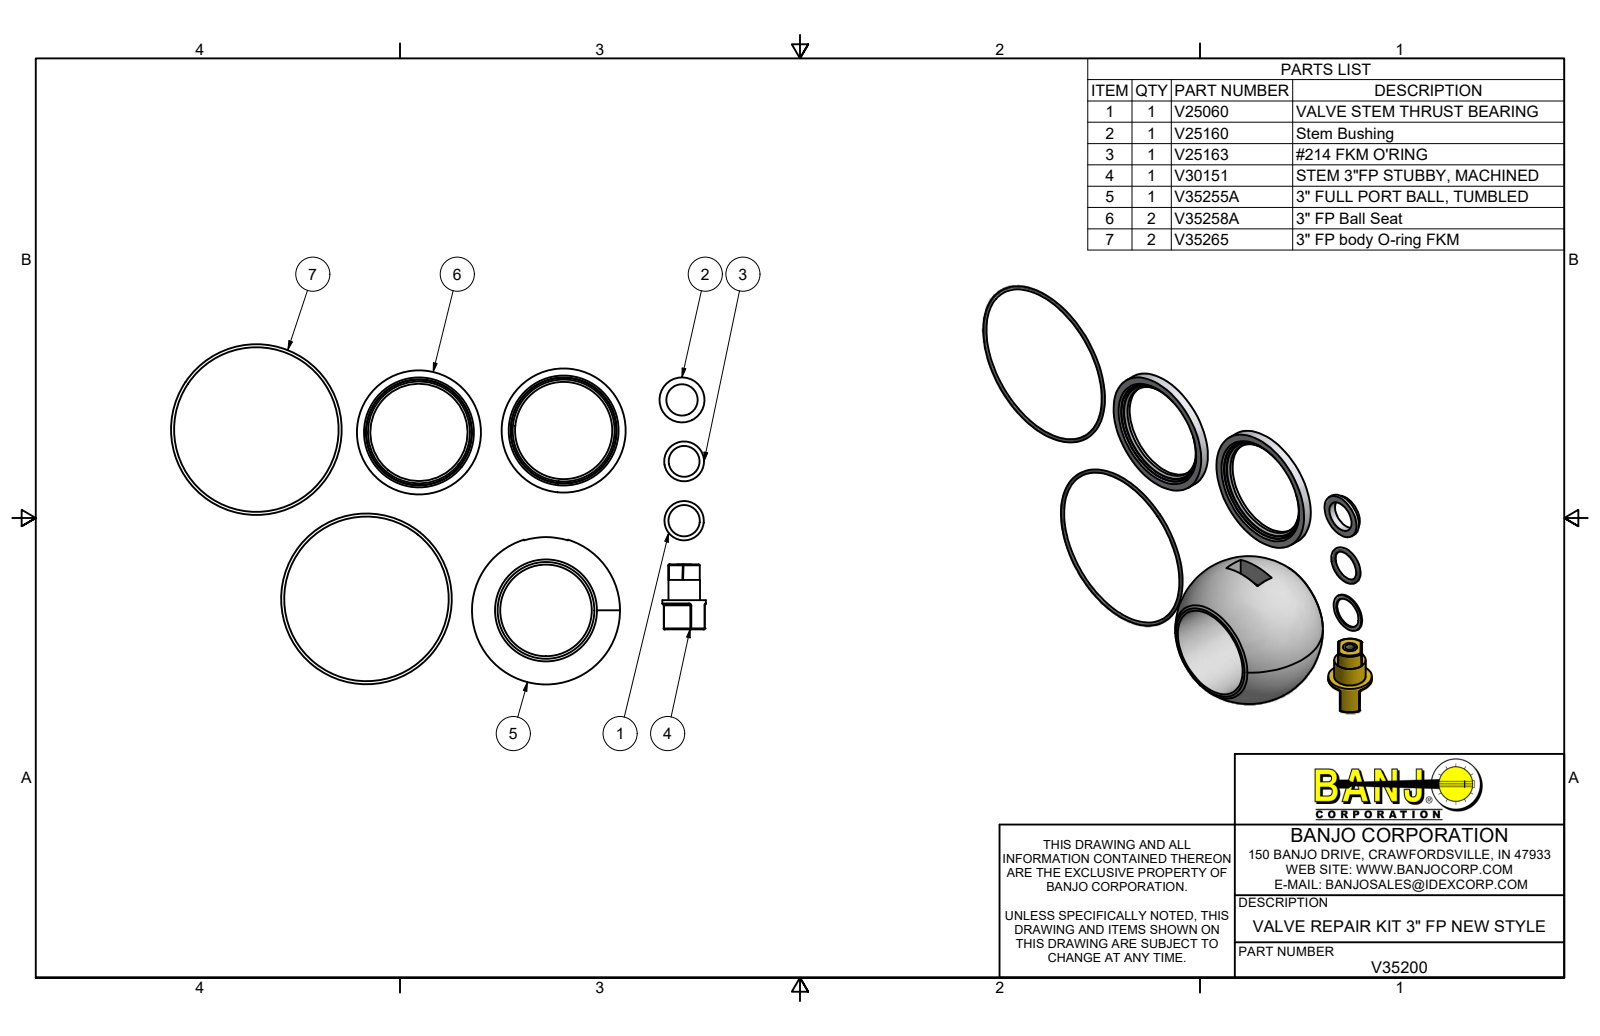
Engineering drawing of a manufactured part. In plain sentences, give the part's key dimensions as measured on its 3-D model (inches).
The part is named "V35200; V25060; V25160; V25163 (+8 more)". Its 3-D file was written by "Autodesk Inventor 2019 (AUTOMOTIVE_DESIGN)". It is 10 solids with 138 faces: 57 planar, 36 cylindrical and 45 other. Overall it measures 17.052 by 10.834 by 3.5 inches. Its volume is 30.39 cubic inches and its surface area 149.6 square inches. Round holes: 2 of diameter 1, 2 of diameter 3.1, 2 of diameter 3.212, 2 of diameter 3.25, 1 of diameter 0.307, 1 of diameter 0.375, 1 of diameter 2.92. Round bosses or shafts: 2 of diameter 3.95, 2 of diameter 3.412, 1 of diameter 1.438, 1 of diameter 1.39, 1 of diameter 1.25, 1 of diameter 1.241, 1 of diameter 1.005, 1 of diameter 0.5. Partial cylindrical surfaces (rounded edges, fillets, slot ends): 10 of radius 0.032, 1 of radius 0.497. The main face-to-face distances are 0.024, 0.3, 0.324, 0.276, 0.313, 0.013, 1.43, 0.079, 0.103, 0.379. The hole center spacings are 3.843, 3.893, 4.614, 4.795, 5.251, 5.756, 6.963, 7.98.
